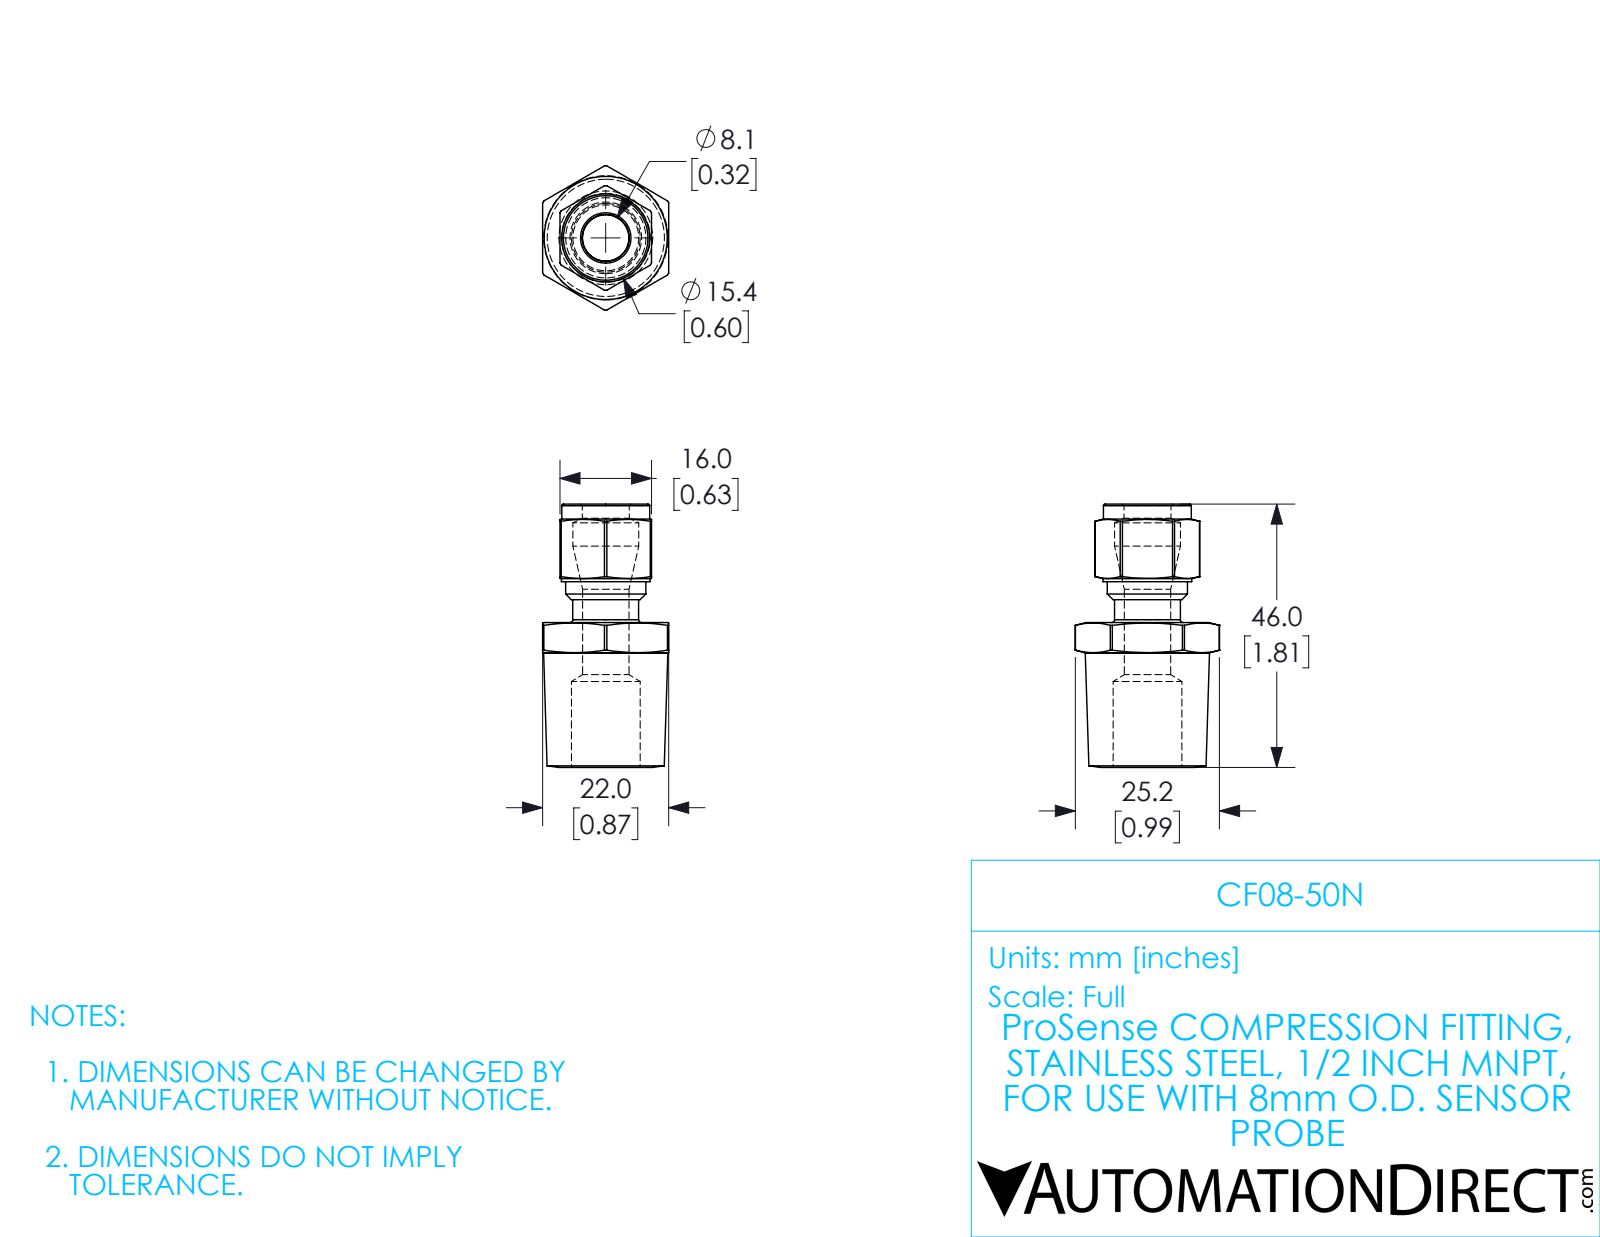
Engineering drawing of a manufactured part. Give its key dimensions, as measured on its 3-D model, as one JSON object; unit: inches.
{"part_name": "CF08-50N", "step_written_by": "SolidWorks 2017 (AUTOMOTIVE_DESIGN)", "units": "inches", "bodies": {"solids": 1, "faces": 75, "planar": 17, "cylindrical": 32, "other": 26}, "overall_size": [1.811, 0.991, 0.866], "volume_in3": 0.56, "surface_area_in2": 7.771, "round_holes": [[0.319, 1], [0.323, 1], [0.453, 1], [0.472, 1]], "round_bosses_or_shafts": [[0.854, 1], [0.61, 1], [0.605, 1], [0.551, 1]], "partial_cylinders_radius": [[0.359, 1], [0.495, 1]], "face_to_face_distances": [0.118, 0.748, 0.63, 0.866, 0.815, 0.996, 1.811, 1.278, 0.281, 0.533]}
